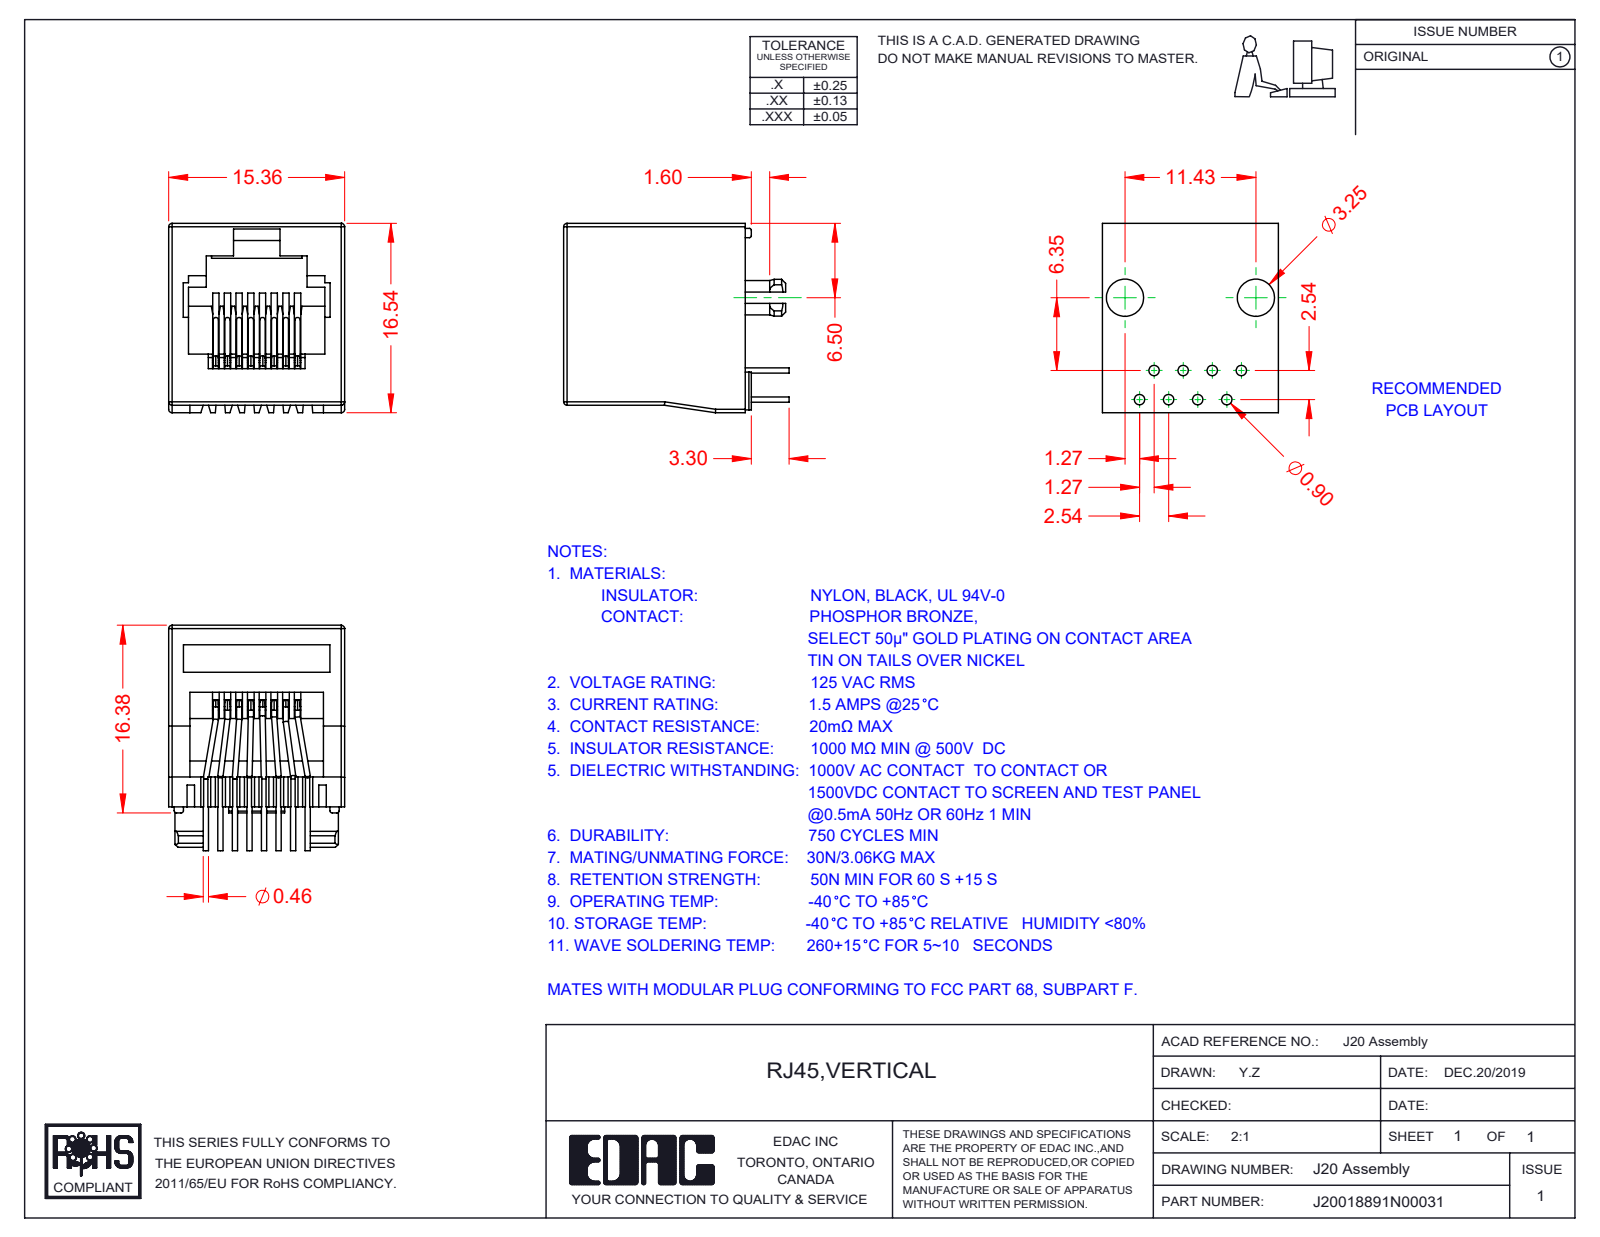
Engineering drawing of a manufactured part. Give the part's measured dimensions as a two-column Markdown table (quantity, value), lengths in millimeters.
| quantity | value |
| --- | --- |
| part name | 20 Insulator; RJ20018891N00031; 20 Contacts |
| STEP written by | SolidWorks 2016 (CONFIG_CONTROL_DESIGN) |
| units | millimeters |
| bodies | 9 solids, 573 faces (332 planar, 193 cylindrical, 48 other) |
| overall size | 19.68 × 16.54 × 15.36 |
| volume | 1 935 mm³ |
| surface area | 3 110 mm² |
| round holes (diameter × count) | 2 × 2 |
| round bosses / shafts (diameter × count) | 0.46 × 45 |
| partial cylindrical surfaces (radius × count) | 0.13 × 16, 0.3 × 13, 0.25 × 9, 0.2 × 5, 0.15 × 2, 1.5 × 2, 1.6 × 2 |
| main face-to-face distances | 15.36, 1.73, 2, 13.63, 0.45, 15.85, 1.28, 10.35, 1.5, 14.08 |
| hole center spacings | 11.43 |
